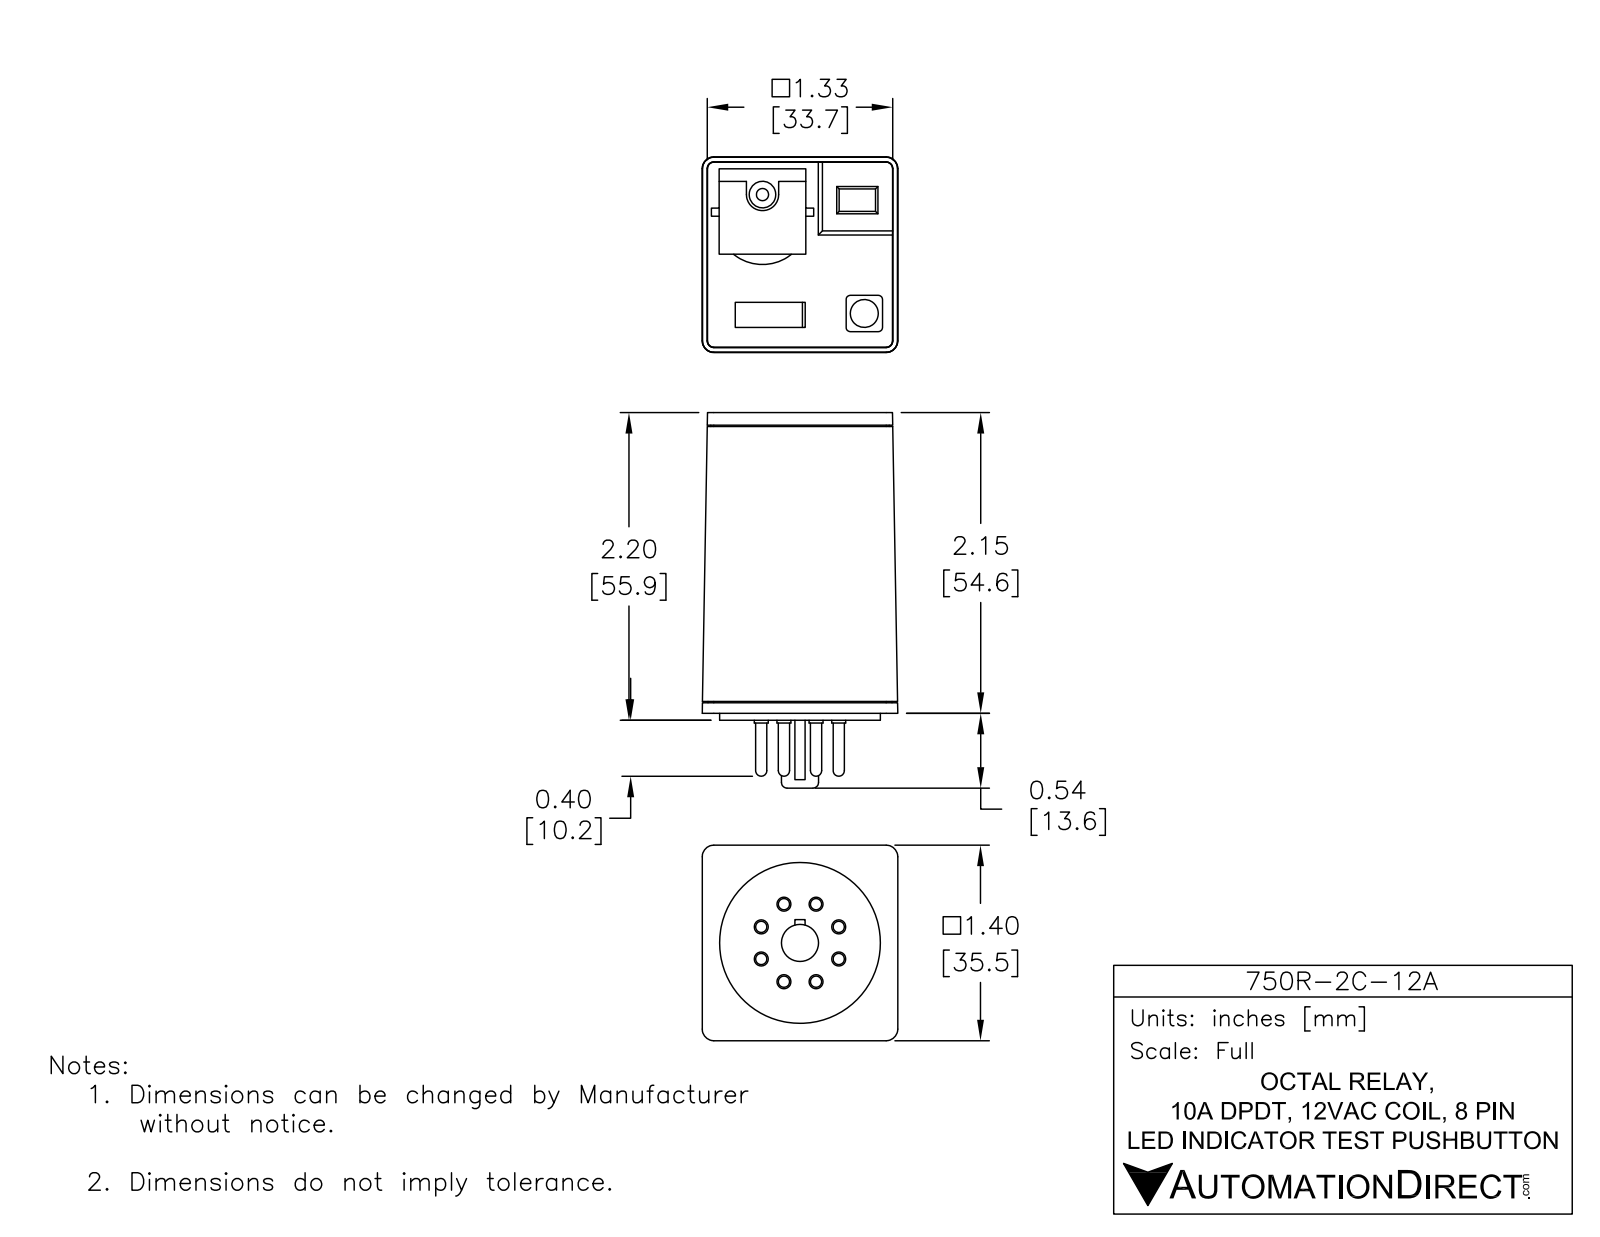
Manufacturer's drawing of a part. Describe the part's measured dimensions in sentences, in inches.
The part is named "750R-2C-12A". Its 3-D file was written by "SolidWorks 2014 (AUTOMOTIVE_DESIGN)". It is 1 solid with 162 faces: 90 planar, 50 cylindrical and 22 other. Overall it measures 2.685 by 1.398 by 1.398 inches. Its volume is 4.047 cubic inches and its surface area 17.37 square inches. Round holes: 1 of diameter 0.087, 1 of diameter 0.2. Round bosses or shafts: 8 of diameter 0.1, 8 of diameter 0.08, 1 of diameter 1.15, 1 of diameter 0.265, 1 of diameter 0.19. Partial cylindrical surfaces (rounded edges, fillets, slot ends): 4 of radius 0.03, 1 of radius 0.115, 1 of radius 0.33. The main face-to-face distances are 0.05, 2.15, 2.2, 2.11, 0.04, 2.19, 2.14, 0.085, 0.03, 2.16. The hole center spacings are 1.119.
